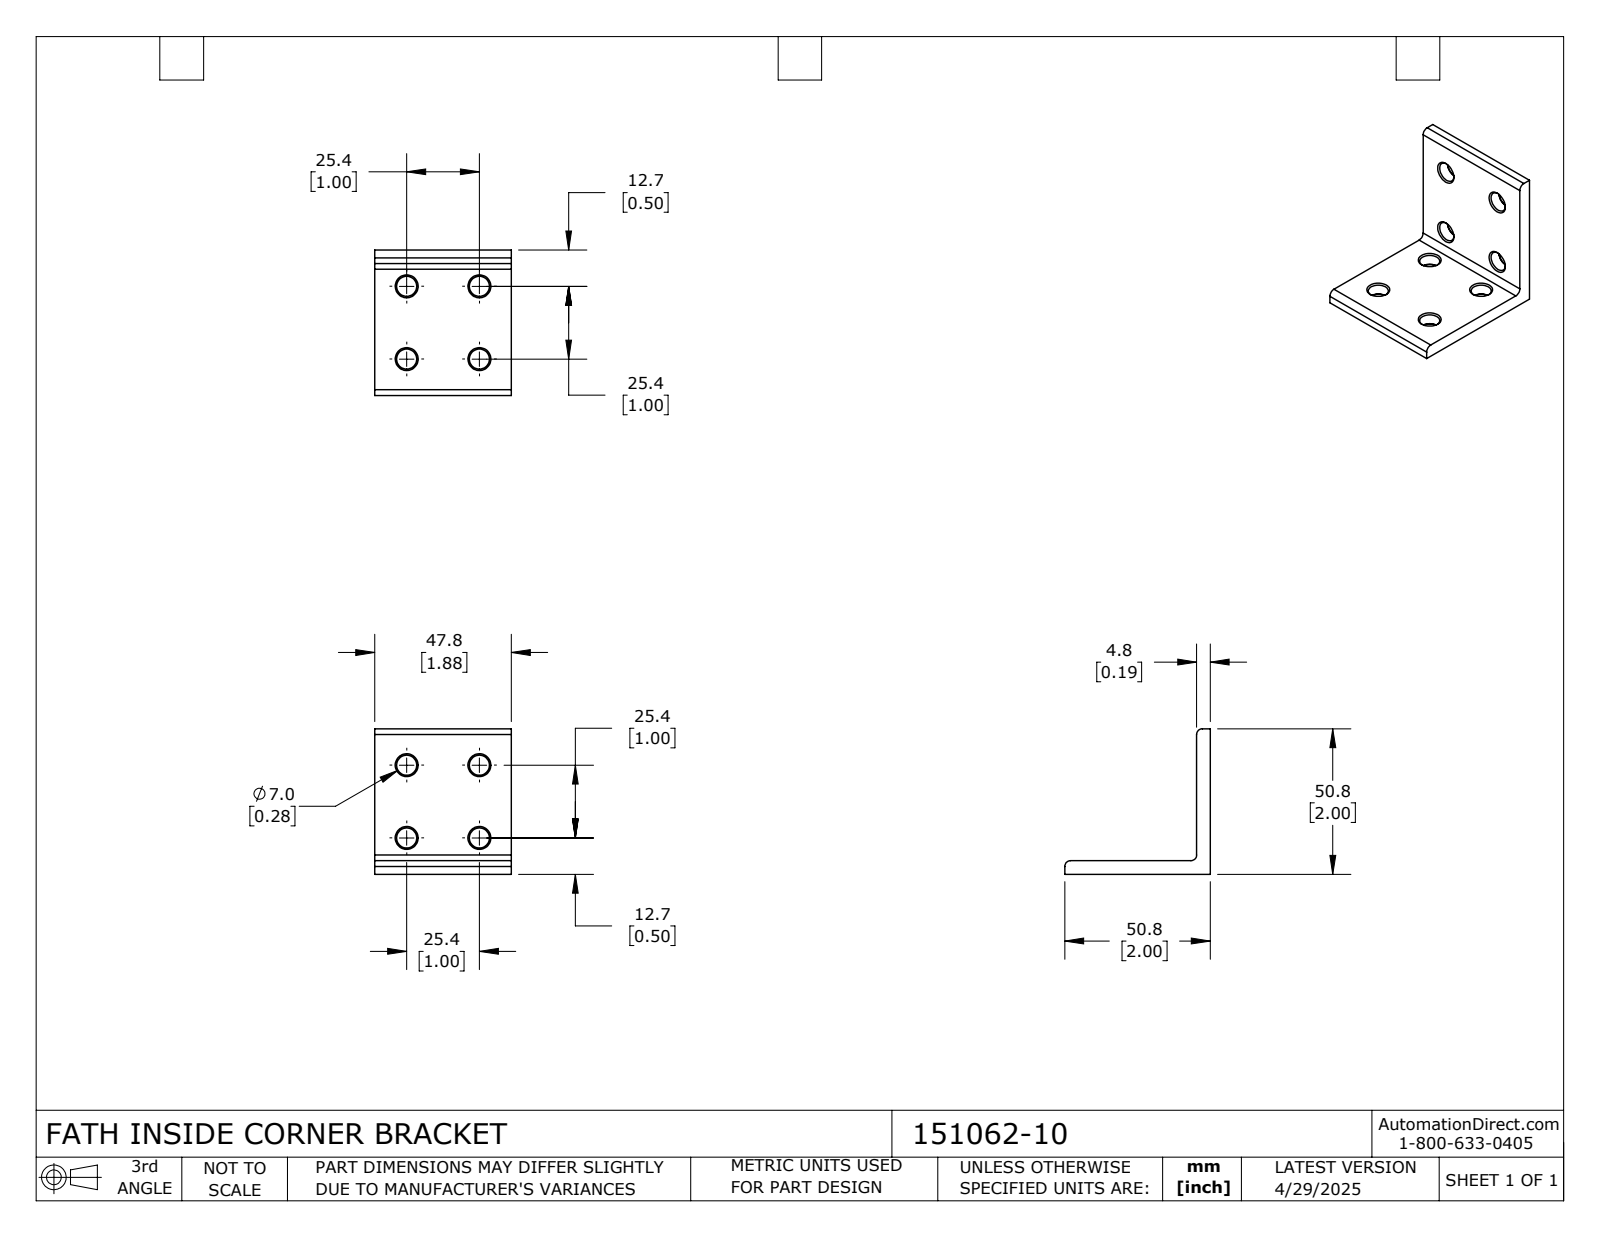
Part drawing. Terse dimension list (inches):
name: 151062-10
written by: SolidWorks 2024 (CONFIG_CONTROL_DESIGN)
unit: in
bodies: 1 solid, 59 faces (8 planar, 19 cylindrical, 32 other)
size: 2 × 2 × 1.88
volume: 1.249 in³; area: 16.47 in²
holes: 8× ⌀0.276
rounds: 3× R0.079
face distances: 0.187, 1.88, 2, 1.813
hole spacings: 1, 1.414
